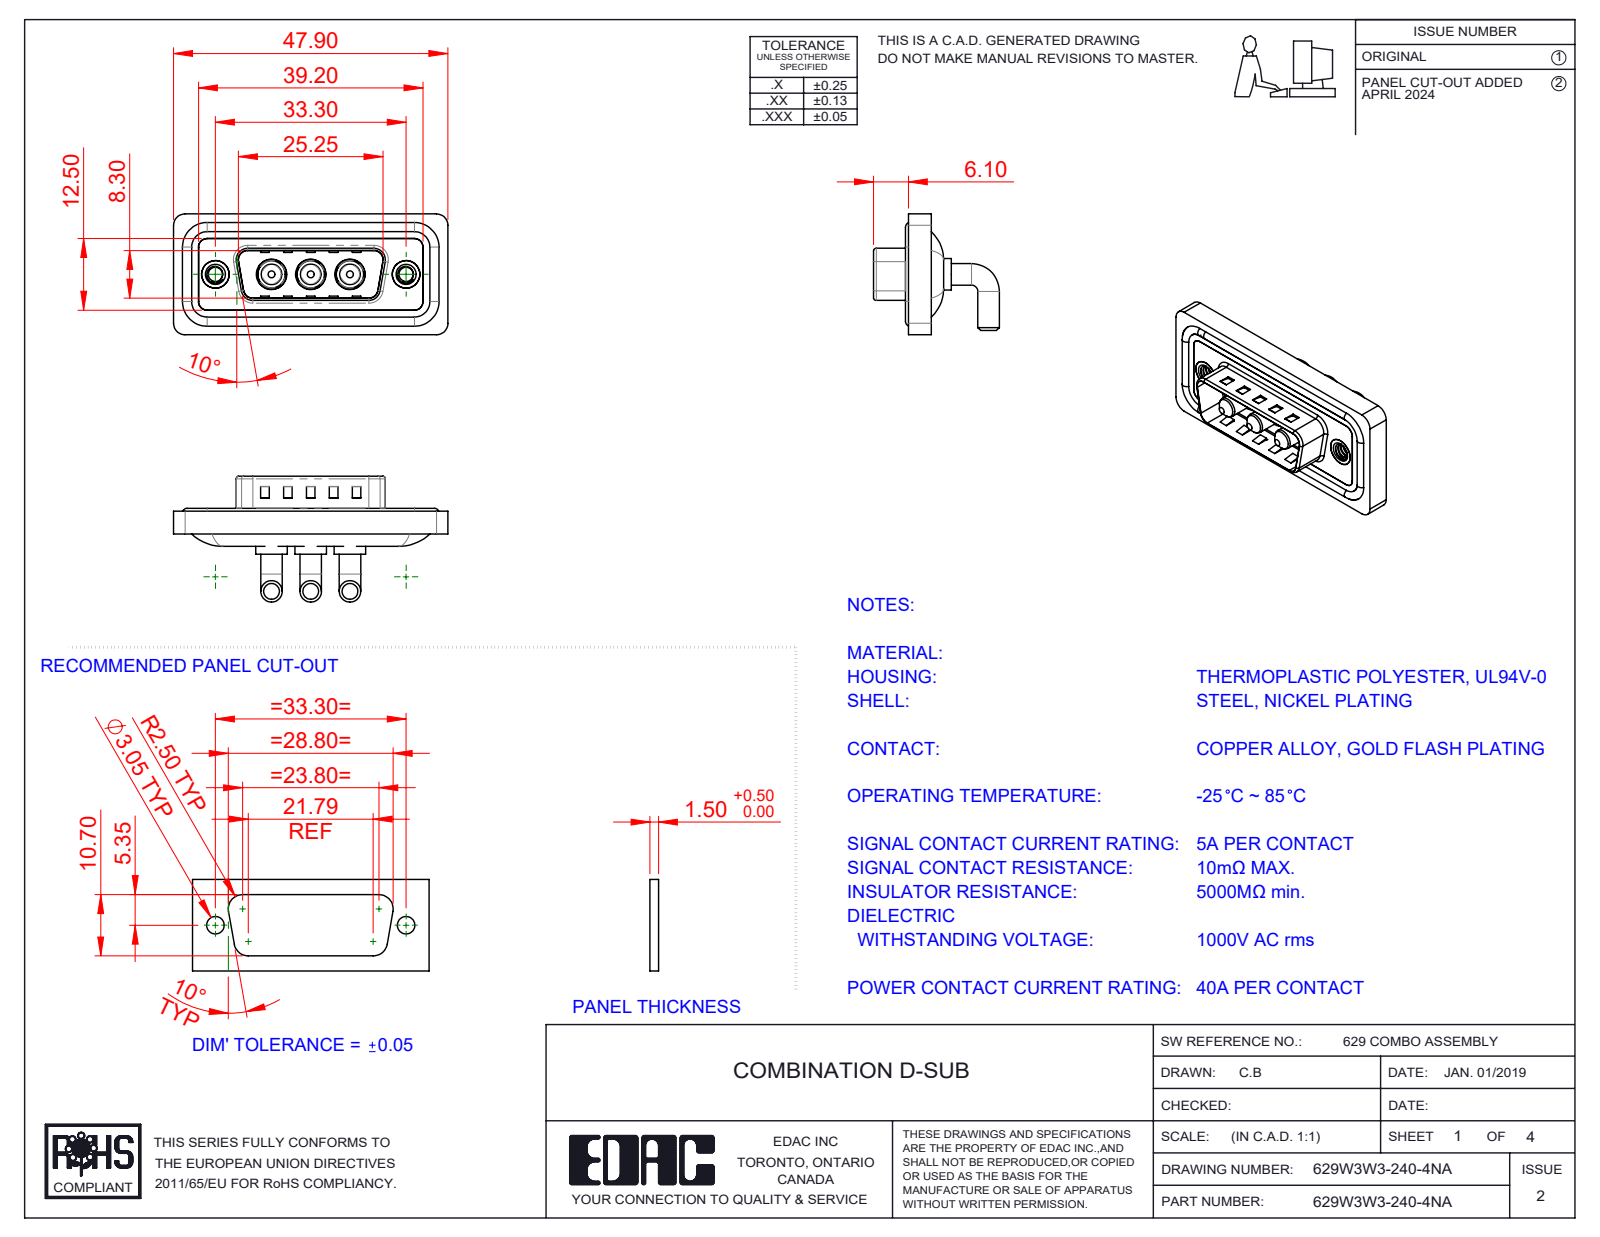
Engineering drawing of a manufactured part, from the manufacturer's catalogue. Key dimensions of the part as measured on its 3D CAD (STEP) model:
Part name (STEP PRODUCT): 629Combo Shell Rear_15 Contacts; 629Combo Housing_3W3; 629Combo Waterproof Housing_15 Contacts; Power Pin_40A RA (+3 more)
STEP written by: SolidWorks 2023 (CONFIG_CONTROL_DESIGN)
Units: millimetres
Bodies: 13 solids, 570 faces (207 planar, 245 cylindrical, 118 other)
Overall size (bounding box): 47.9 × 21.98 × 21.1
Volume: 6 001 mm³ · Surface area: 9 171 mm²
Round holes (diameter × count): ⌀4.85 ×3, ⌀5.3 ×3, ⌀2.5 ×2, ⌀4 ×2, ⌀4.8 ×2, ⌀5 ×2
Round bosses / shafts (diameter × count): ⌀3.75 ×6, ⌀1.6 ×4, ⌀5.5 ×3, ⌀5.2 ×3, ⌀4.75 ×3, ⌀3.6 ×3, ⌀4.9 ×2
Partial cylindrical surfaces — rounded edges, fillets, slot ends (radius × count): R2 ×20, R1.5 ×18, R0.5 ×8, R1.6 ×8, R0.25 ×4, R0.6 ×4, R0.65 ×4, R0.9 ×4
Main face-to-face distances: 0.4, 2.9, 0.8, 1.1, 2.1, 1.6, 3.1, 2.5, 4.5, 3.7
Hole centre spacings: 6.85, 9.8, 16.65, 23.5, 13.7, 33.3
